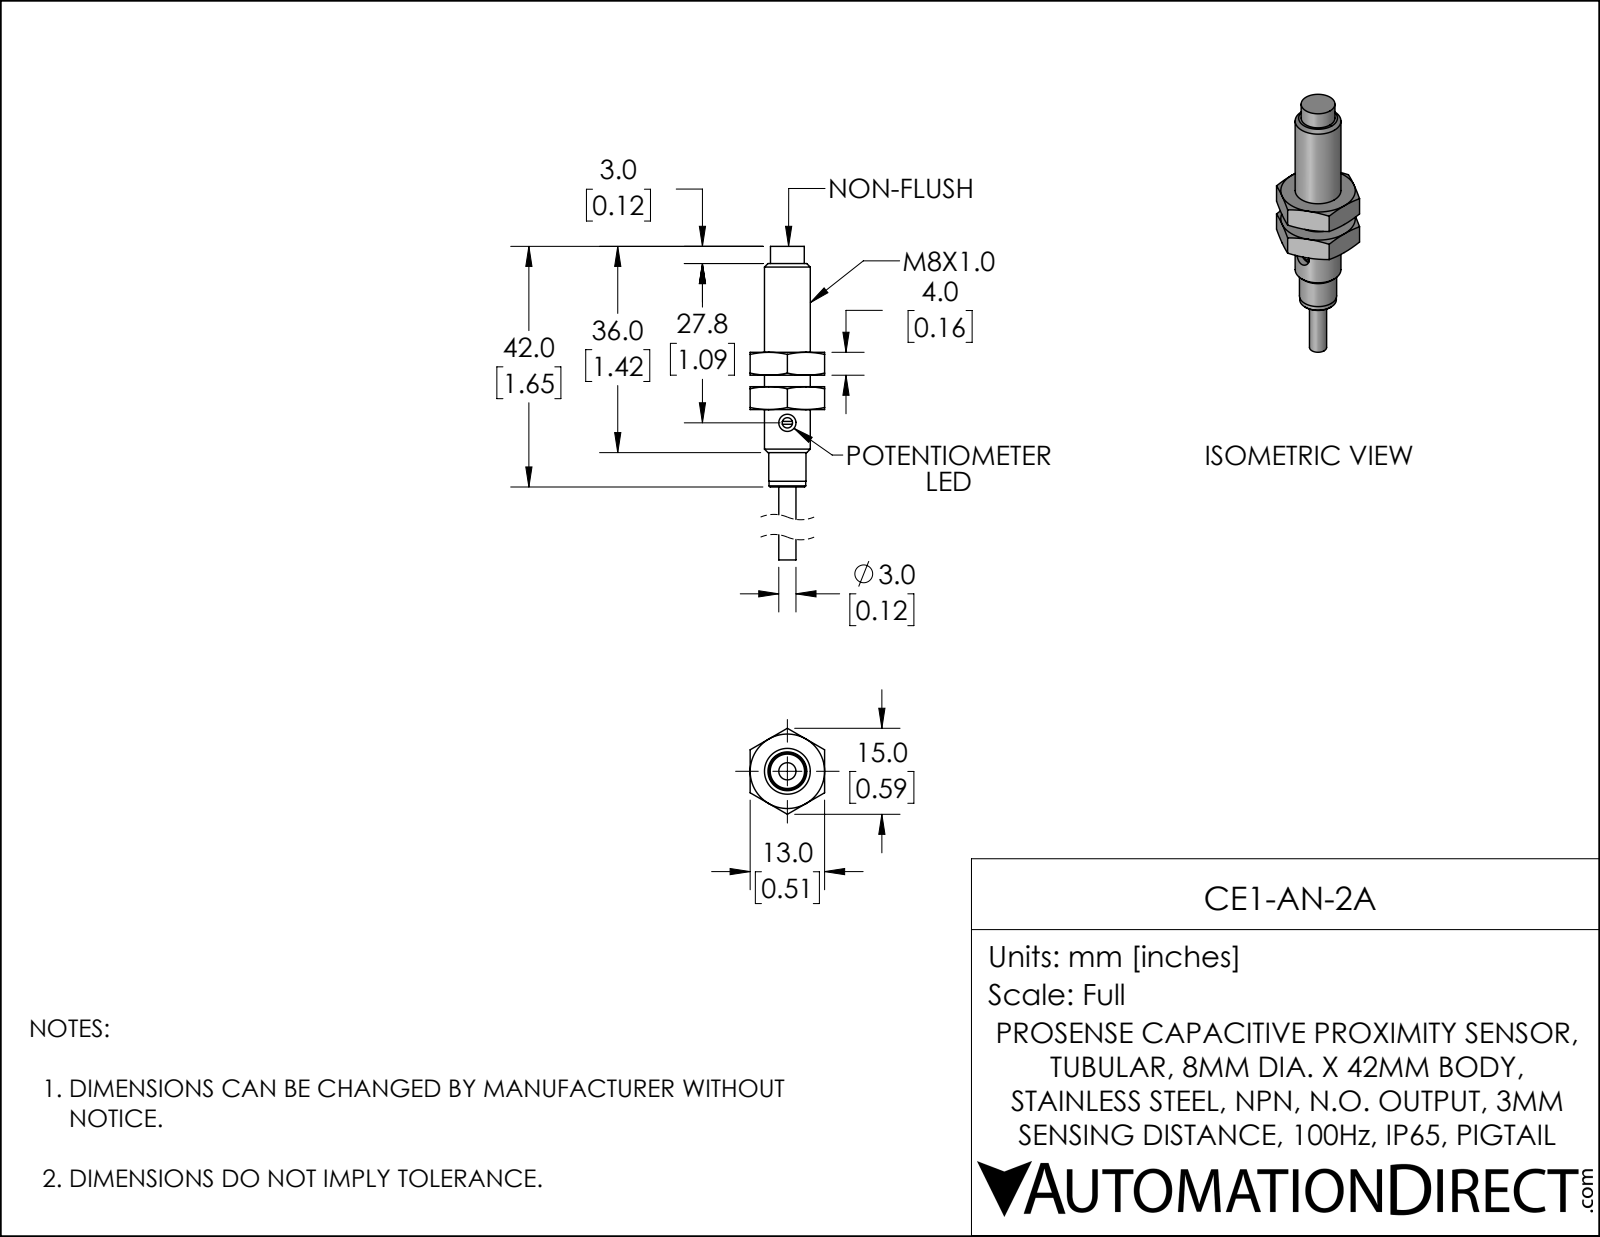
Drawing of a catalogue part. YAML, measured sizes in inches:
part_name: "CE1-AN-2A"
step_written_by: "SolidWorks 2019 (CONFIG_CONTROL_DESIGN)"
units: inches
bodies: {solids: 3, faces: 68, planar: 28, cylindrical: 9, other: 31}
overall_size: [2.047, 0.591, 0.512]
volume: 0.174
surface_area: 3.281
round_holes:
  - {diameter: 0.118, count: 1}
  - {diameter: 0.272, count: 1}
round_bosses_or_shafts:
  - {diameter: 0.315, count: 1}
  - {diameter: 0.256, count: 1}
  - {diameter: 0.252, count: 1}
  - {diameter: 0.232, count: 1}
  - {diameter: 0.118, count: 1}
  - {diameter: 0.071, count: 1}
face_to_face_distances: [0.512, 0.236, 0.157, 0.394, 0.079, 0.926, 0.728, 0.885, 0.964, 1.122]
